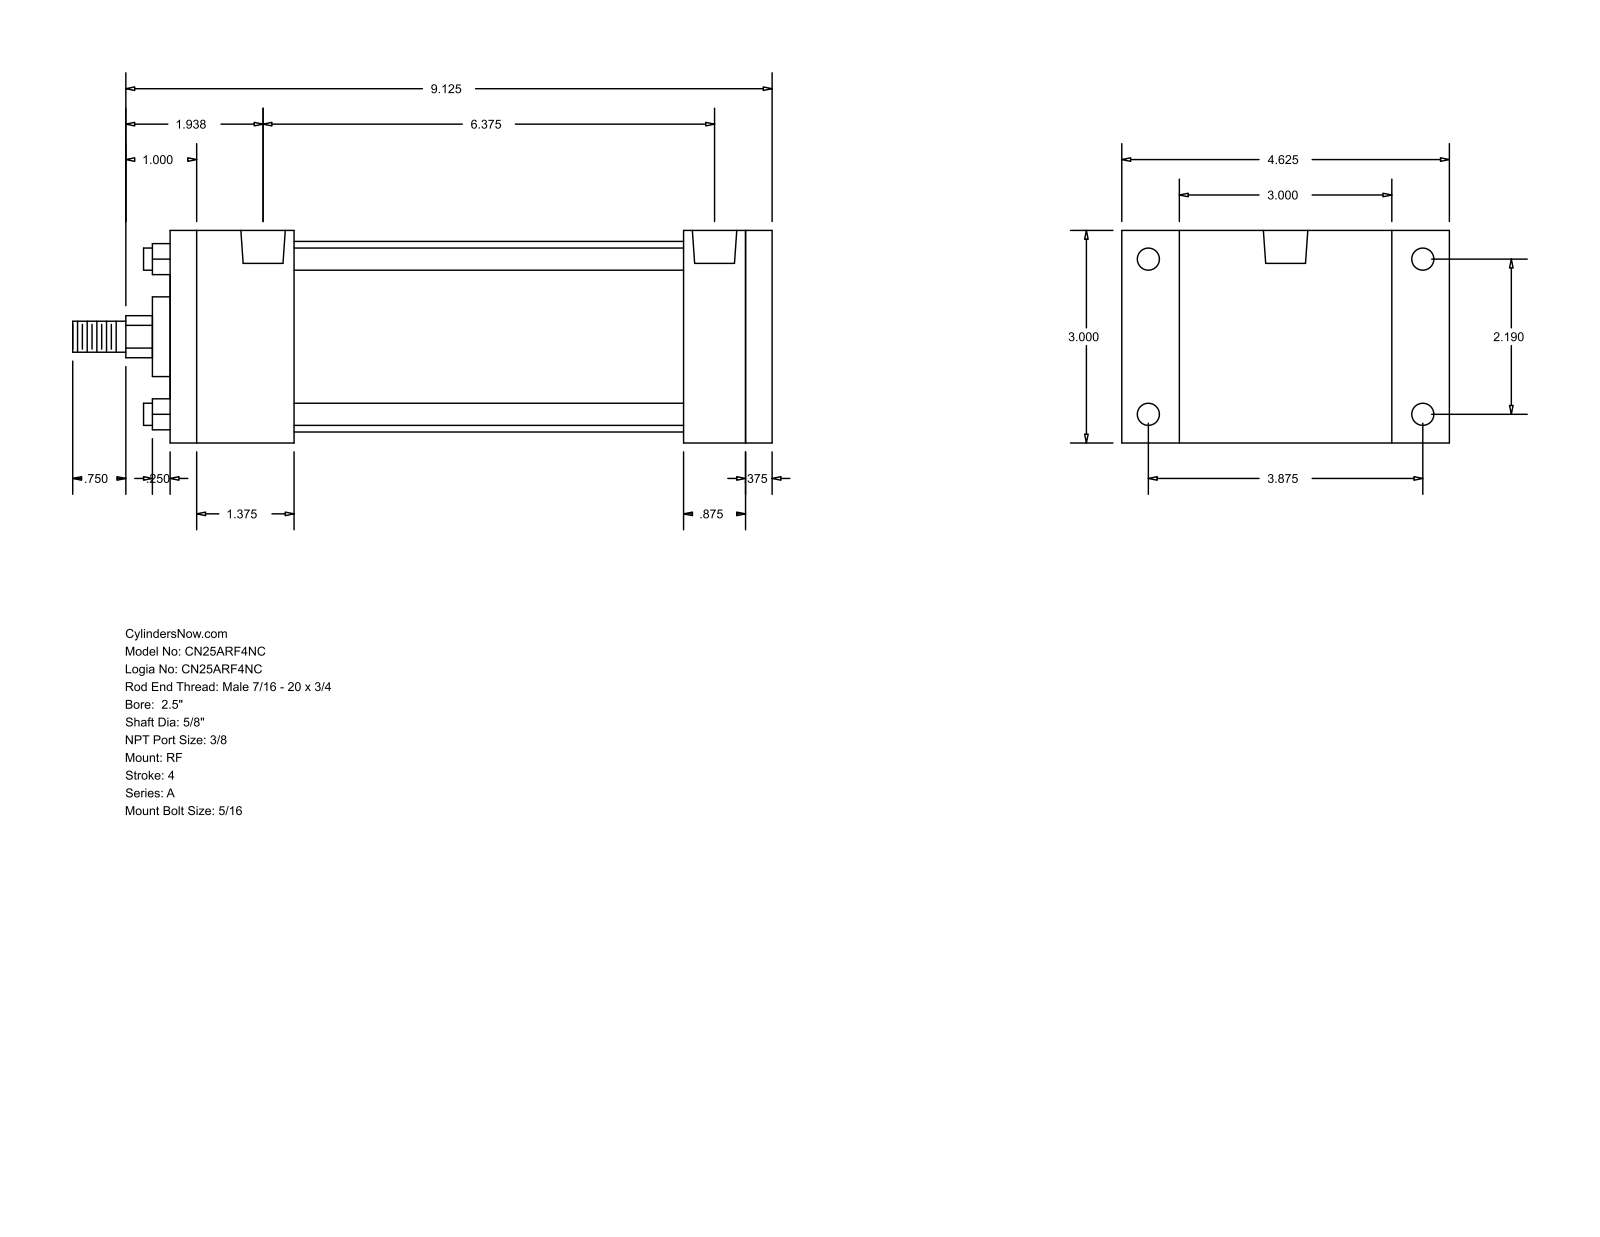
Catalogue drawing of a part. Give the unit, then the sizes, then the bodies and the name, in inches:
Units: inches
Overall size (bounding box): 9.875 × 4.625 × 3
Round holes (diameter × count): ⌀0.219 ×4, ⌀0.313 ×4, ⌀0.627 ×2
Round bosses / shafts (diameter × count): ⌀0.313 ×4, ⌀2.69 ×1, ⌀1.125 ×1, ⌀0.625 ×1, ⌀0.437 ×1
Partial cylindrical surfaces — rounded edges, fillets, slot ends (radius × count): R0.297 ×1
Main face-to-face distances: 3, 8.5, 0.375, 8.125, 1.75, 1.25, 7.25, 5.5, 6.375, 6.75
Hole centre spacings: 0.094, 2.19, 3.875, 4.451, 6.469, 6.563, 6.375
Bodies: 0 solids, 92 faces (64 planar, 28 cylindrical, 0 other)
Part name (STEP PRODUCT): A_RF__0250_0.625
STEP written by: GSSL Pune (CONFIG_CONTROL_DESIGN)
